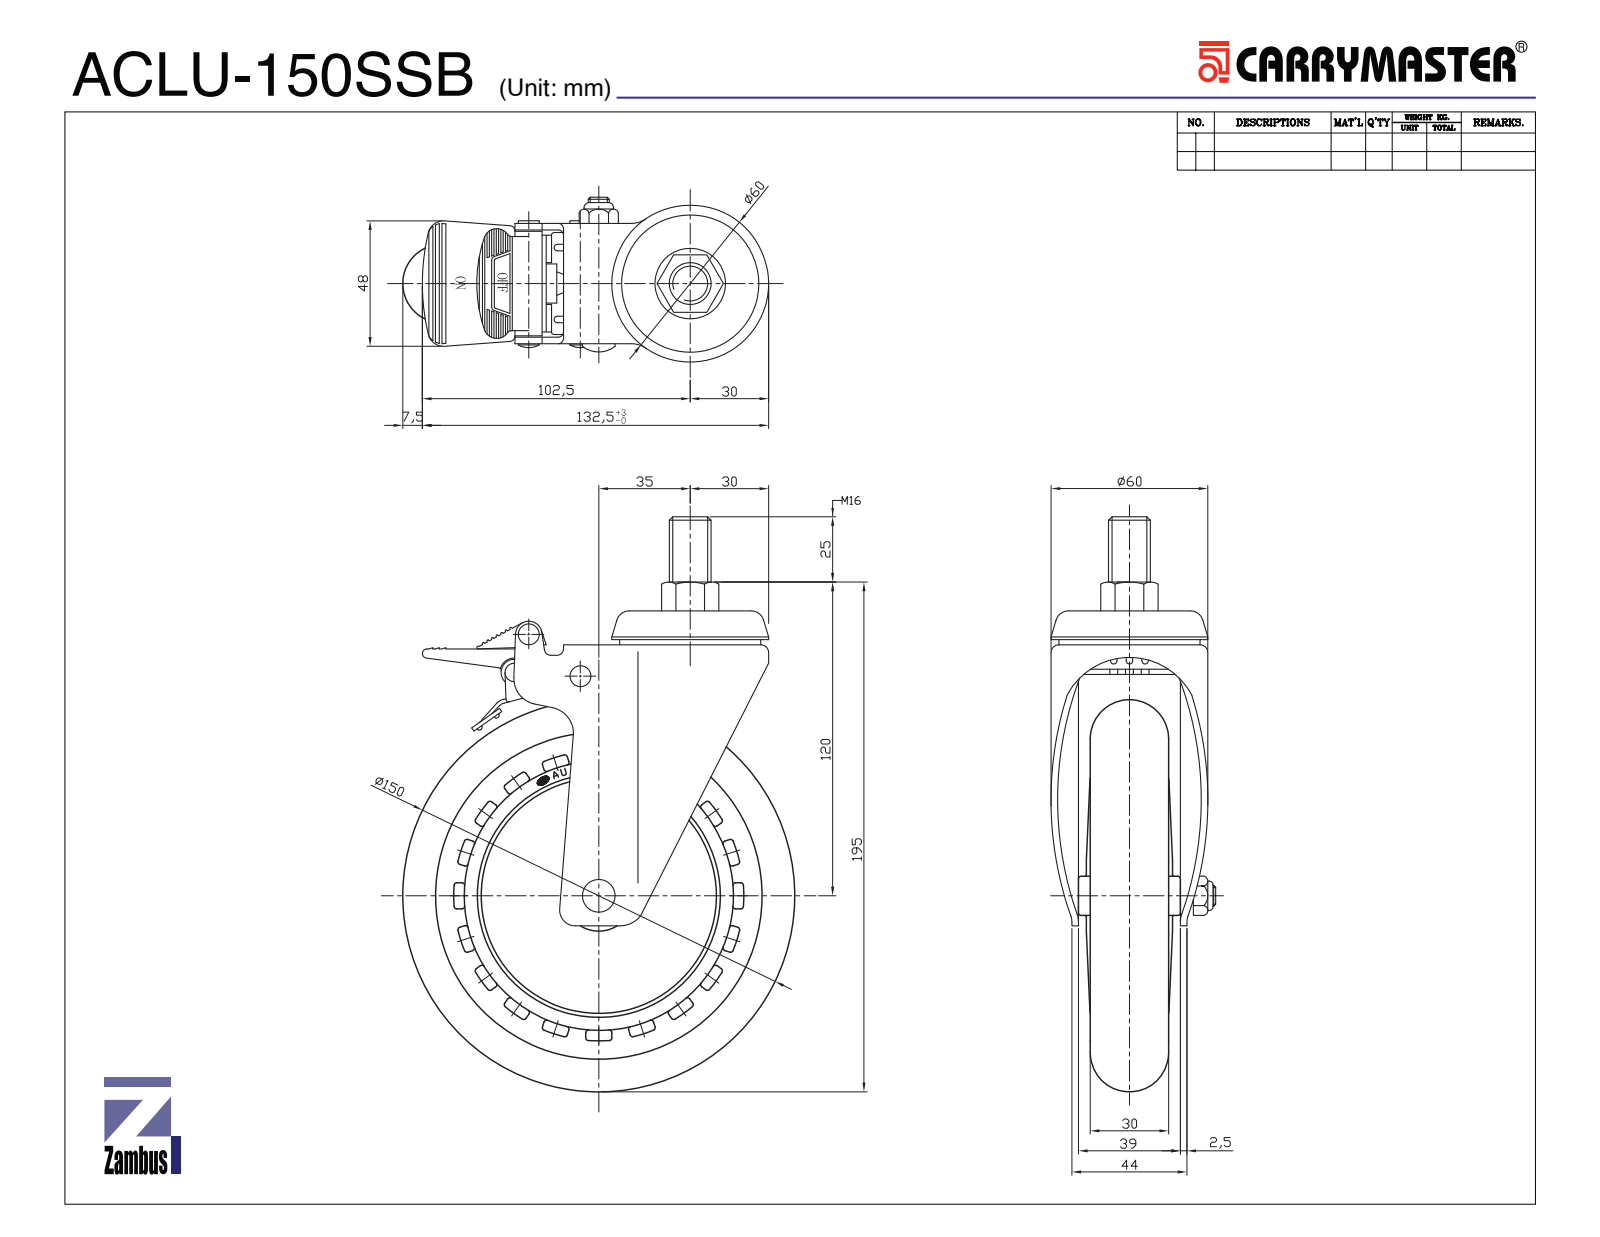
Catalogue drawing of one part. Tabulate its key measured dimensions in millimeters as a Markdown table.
| quantity | value |
| --- | --- |
| part name | ACLU-150SSB |
| STEP written by | SolidWorks 2015 (CONFIG_CONTROL_DESIGN) |
| units | millimeters |
| bodies | 23 solids, 1612 faces (825 planar, 488 cylindrical, 299 other) |
| overall size | 221.52 × 150 × 61.4 |
| volume | 477 249 mm³ |
| surface area | 191 669 mm² |
| round holes (diameter × count) | 3.5 × 2, 4.3 × 2, 5.2 × 2, 5.3 × 1, 6.8 × 1, 8 × 1, 9.6 × 1, 12.6 × 1, 19.6 × 1, 22 × 1, 28.62 × 1, 29.82 × 1 |
| round bosses / shafts (diameter × count) | 16 × 2, 9 × 2, 4.9 × 2, 120 × 1, 90 × 1, 59.7 × 1, 40 × 1, 32 × 1 |
| partial cylindrical surfaces (radius × count) | 1 × 91, 0.2 × 20, 3.86 × 19, 46.25 × 16, 2 × 6, 2.5 × 4, 3 × 4, 10 × 4 |
| main face-to-face distances | 30.5, 12.3, 18.7, 11.8, 0.5, 18.2, 2.5, 5, 5.5, 7.5 |
| hole center spacings | 17.48, 9.7, 12.81, 25.75, 26.08, 84.49, 89.54, 91.03 |
